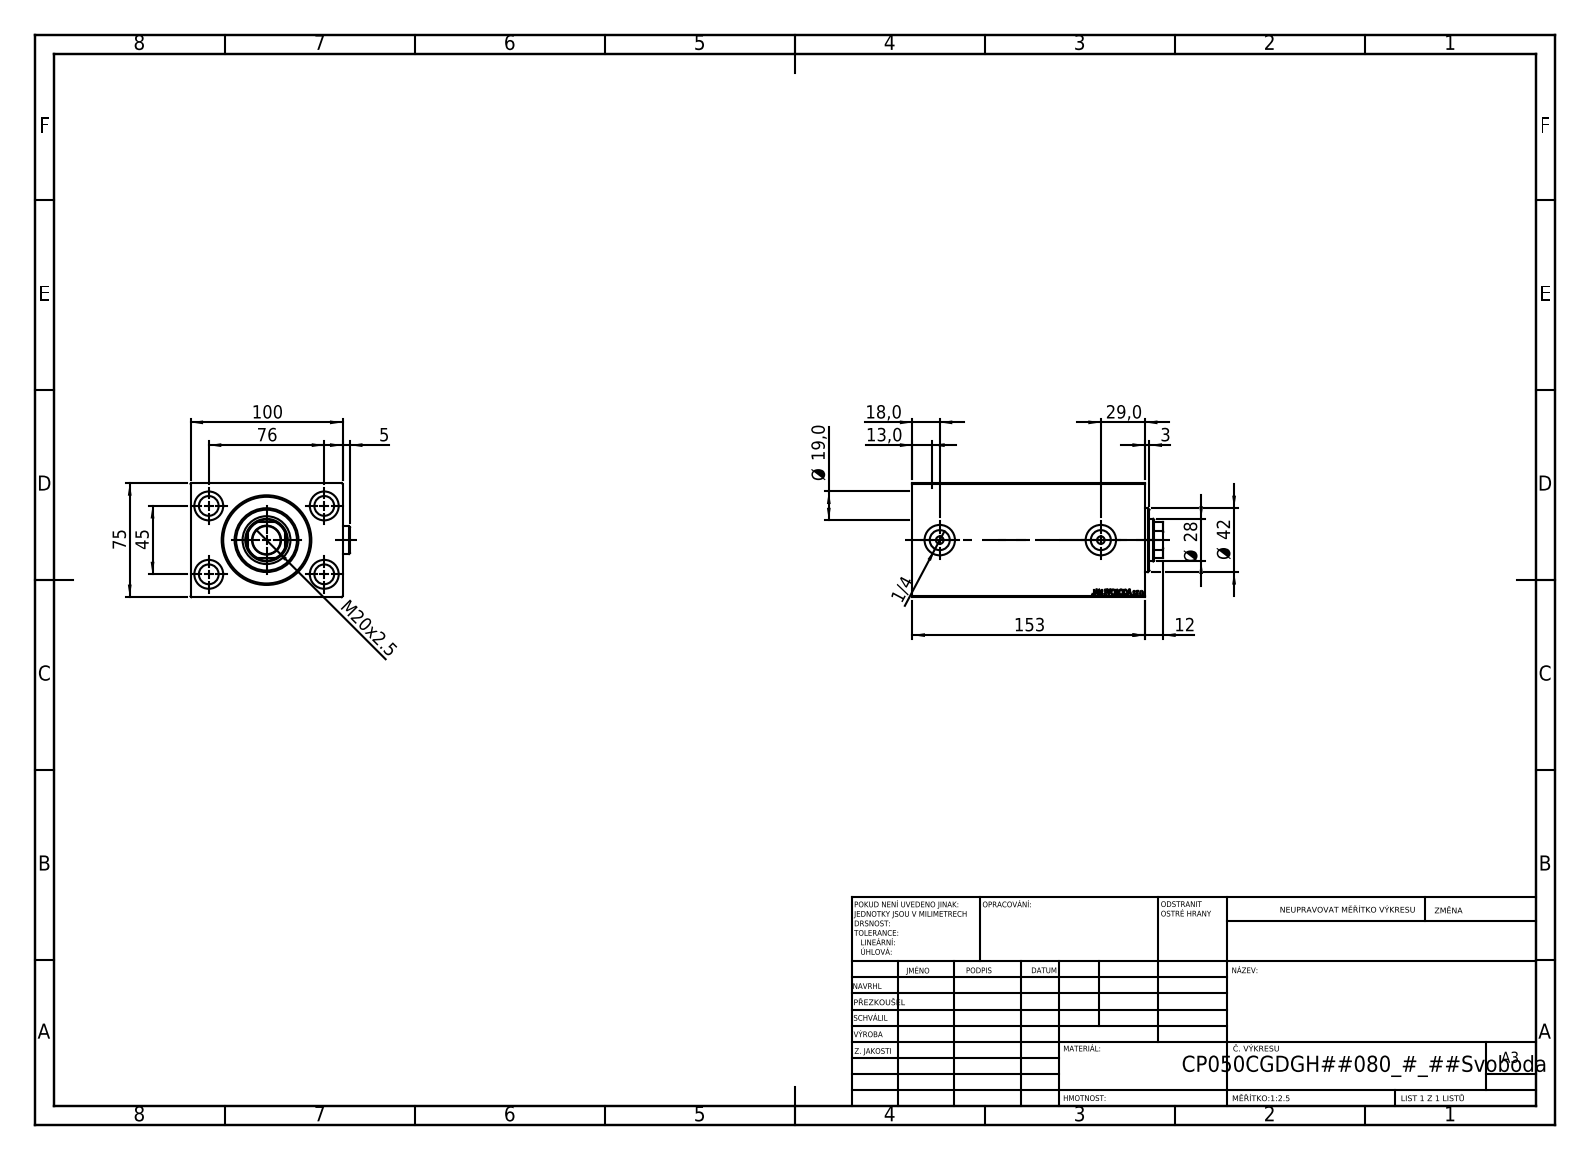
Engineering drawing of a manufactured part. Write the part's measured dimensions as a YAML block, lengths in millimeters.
part_name: "V450CM_C_Body; V450CM_C_VCP; V450CM_VC_B; Zatka_OIL_PORT"
step_written_by: "SolidWorks 2019 (CONFIG_CONTROL_DESIGN)"
units: millimeters
bodies: {solids: 5, faces: 919, planar: 443, cylindrical: 78, other: 398}
overall_size: [165, 104.9, 75]
volume: 938360
surface_area: 150181
round_holes:
  - {diameter: 13, count: 4}
  - {diameter: 19, count: 4}
  - {diameter: 5, count: 2}
  - {diameter: 13.16, count: 2}
  - {diameter: 20, count: 2}
  - {diameter: 18.5, count: 1}
  - {diameter: 28, count: 1}
  - {diameter: 31.5, count: 1}
  - {diameter: 50, count: 1}
  - {diameter: 52, count: 1}
  - {diameter: 57, count: 1}
round_bosses_or_shafts:
  - {diameter: 18, count: 2}
  - {diameter: 42, count: 1}
partial_cylinders:
  - {radius: 13.5, count: 1}
face_to_face_distances: [75, 100, 153, 14, 139, 127, 12, 141, 13, 47]
hole_center_spacings: [44.16, 45, 76, 88.32, 106]
